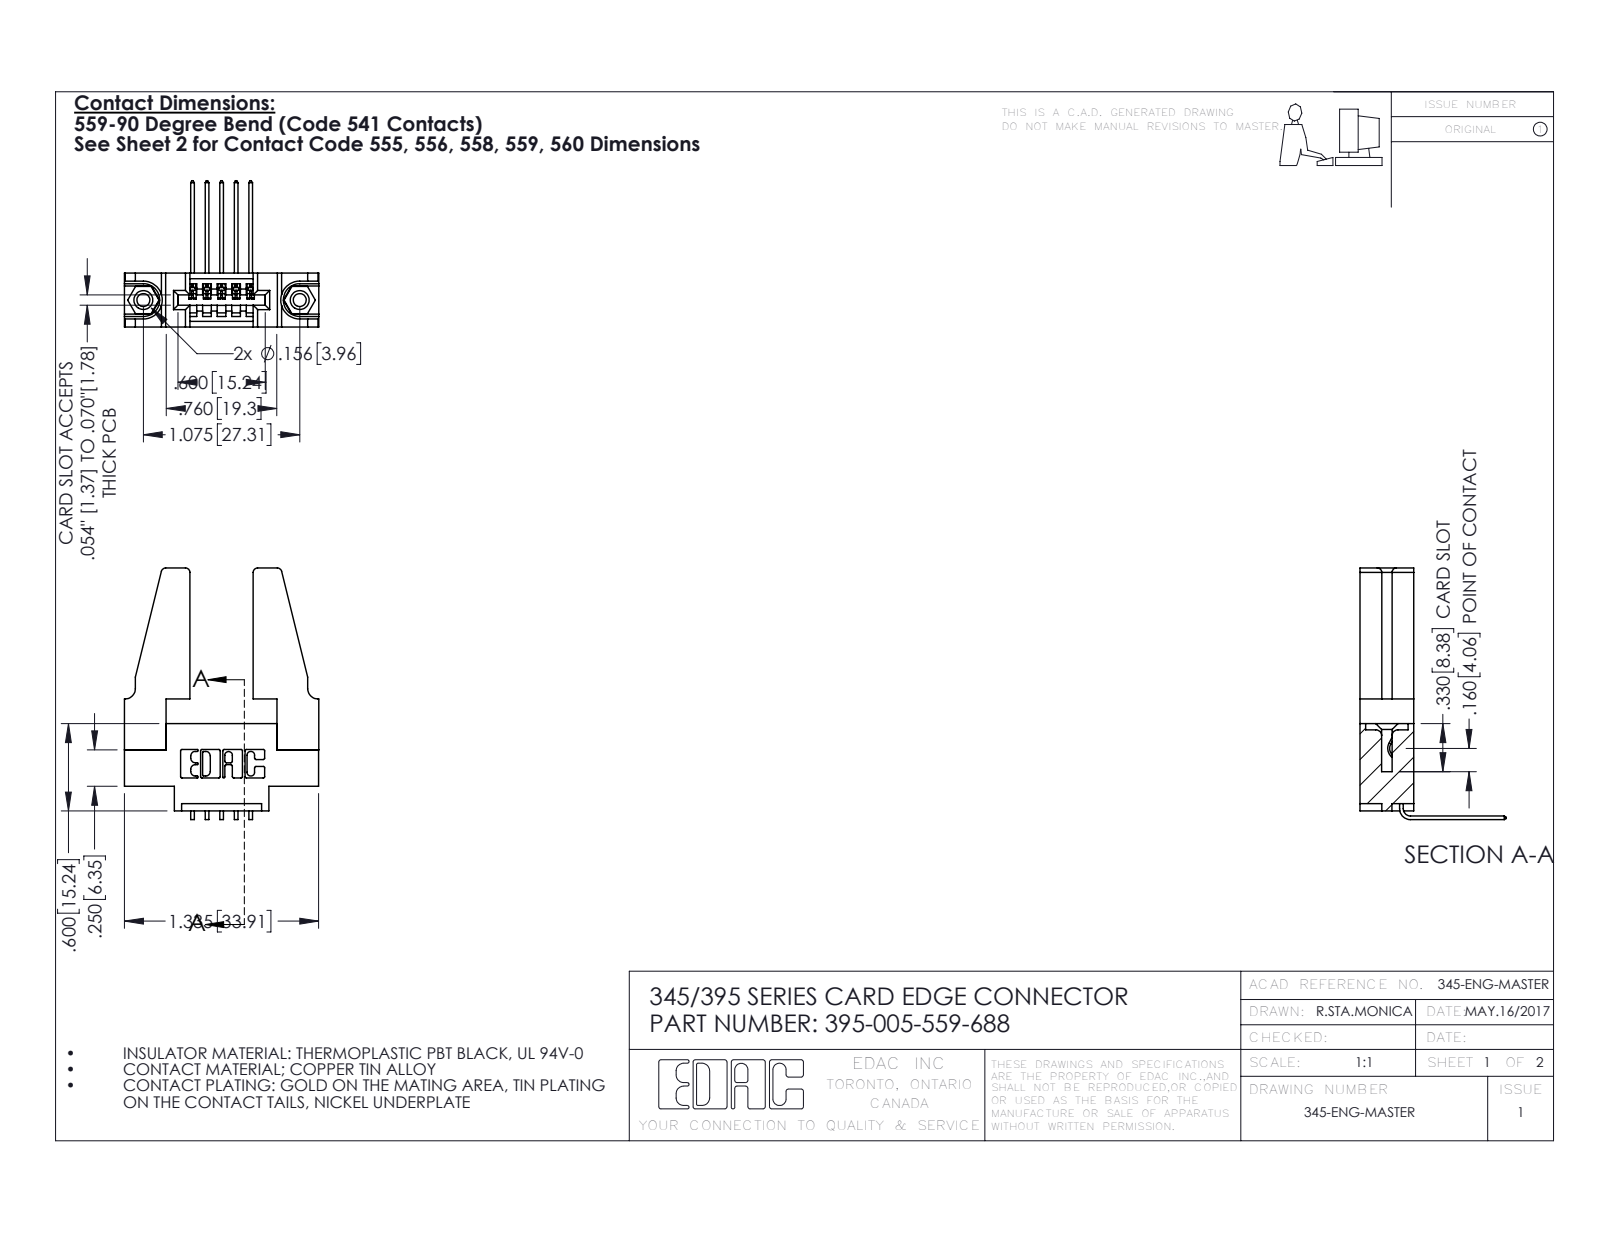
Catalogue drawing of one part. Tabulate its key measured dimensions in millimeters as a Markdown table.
| quantity | value |
| --- | --- |
| part name | 345-220-078_345-220-088; 345-292-001_558 559 Tail - 1; 345 Part_0.170 Offset - 0.156 Dia-TH; 395-005-559-688 (+1 more) |
| STEP written by | SolidWorks 2016 (CONFIG_CONTROL_DESIGN) |
| units | millimeters |
| bodies | 10 solids, 554 faces (366 planar, 172 cylindrical, 16 other) |
| overall size | 43.9 × 33.9 × 25.5 |
| volume | 6 080 mm³ |
| surface area | 6 600 mm² |
| round holes (diameter × count) | 2.3 × 2, 3.2 × 2, 4 × 2, 1.6 × 1 |
| round bosses / shafts (diameter × count) | 3.9 × 2 |
| partial cylindrical surfaces (radius × count) | 0.3 × 22, 0.2 × 10, 0.8 × 8, 0.2 × 6, 0.8 × 6, 0.7 × 3, 0.8 × 2, 1 × 2 |
| main face-to-face distances | 9.4, 1.8, 7.6, 5.1, 3.8, 3.8, 5.6, 2, 11, 7.3 |
| hole center spacings | 6.9, 21.5, 27.3 |
